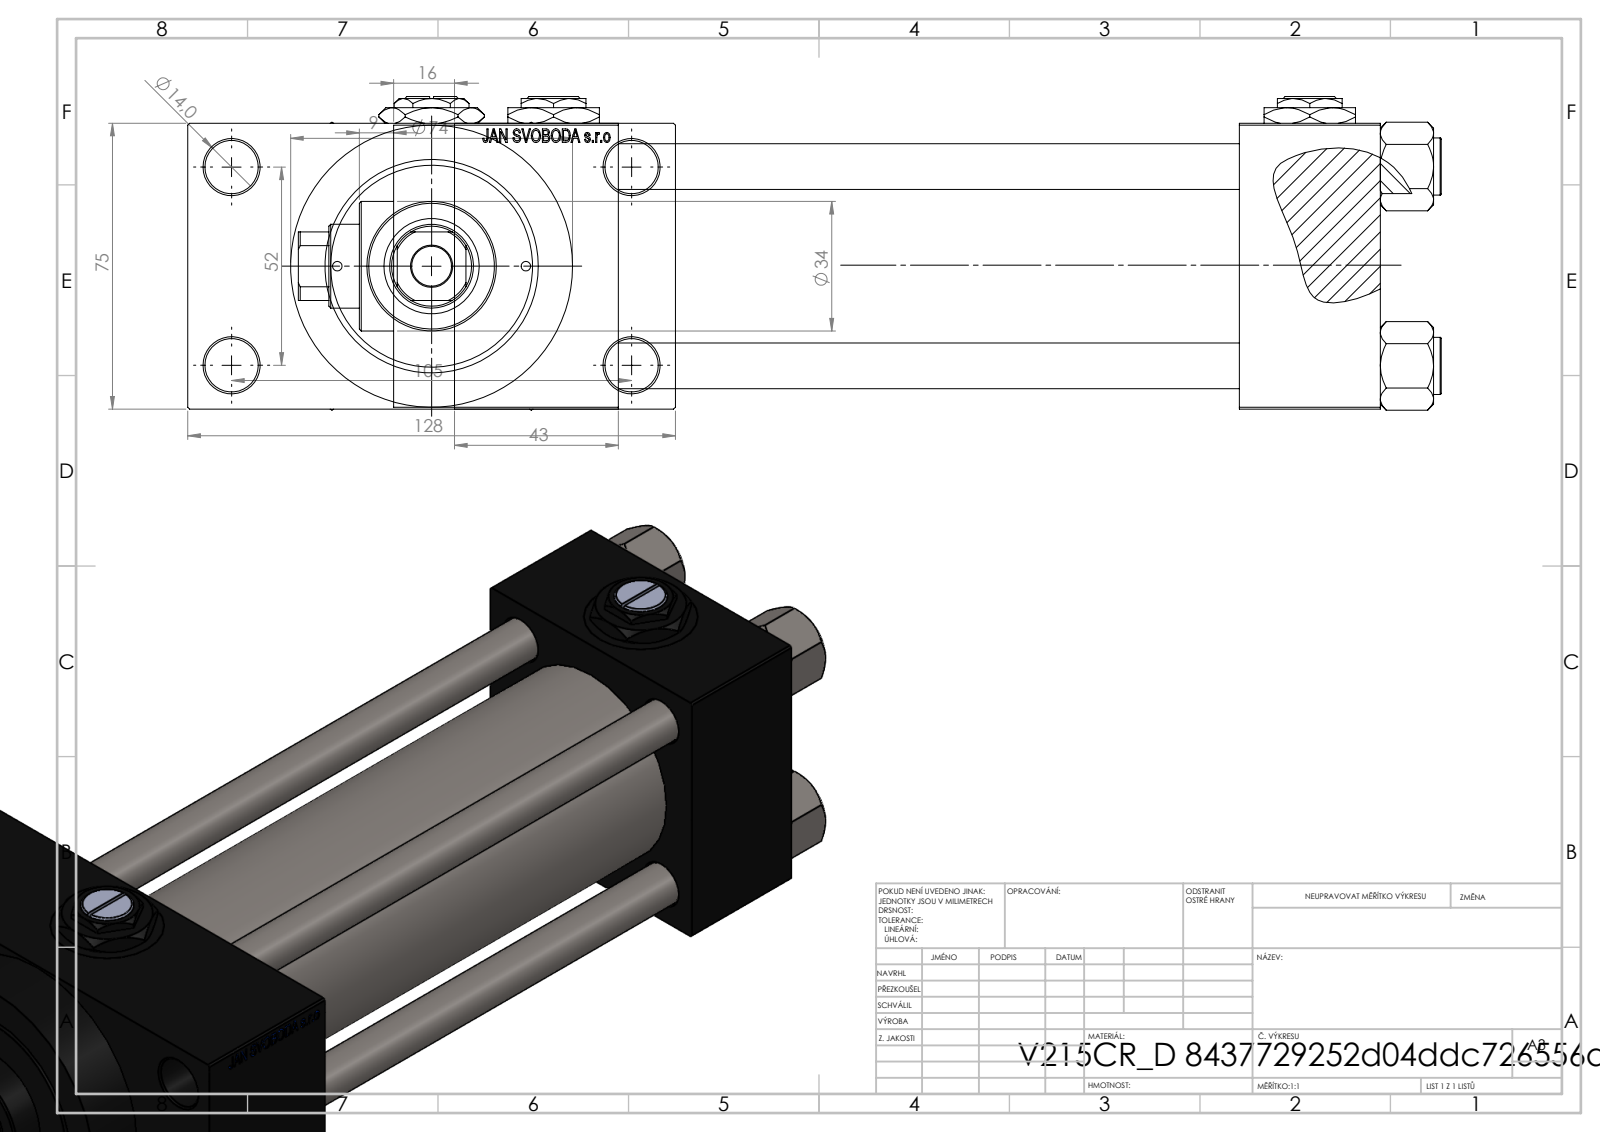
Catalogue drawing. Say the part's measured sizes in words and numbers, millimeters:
The part is named "V215_VC_A; V215CR_D_TYCINKA; V215CR_D_Body; NUT_M5_D (+2 more)". Its 3-D file was written by "SolidWorks 2019 (CONFIG_CONTROL_DESIGN)". It is 13 solids with 1212 faces: 547 planar, 103 cylindrical and 562 other. Overall it measures 300 by 128 by 82.27 millimeters. Its volume is 932 755 cubic millimeters and its surface area 228 913 square millimeters. Round holes: 4 of diameter 12, 4 of diameter 14, 4 of diameter 20.96, 4 of diameter 30, 3 of diameter 7, 2 of diameter 2.5, 1 of diameter 10.5, 1 of diameter 22, 1 of diameter 25, 1 of diameter 41, 1 of diameter 50, 1 of diameter 53. Round bosses or shafts: 4 of diameter 15, 1 of diameter 74, 1 of diameter 56, 1 of diameter 34. Partial cylindrical surfaces (rounded edges, fillets, slot ends): 1 of radius 10.5. The main face-to-face distances are 75, 163, 37, 200, 26.5, 243, 206, 43, 101.5, 16. The hole center spacings are 26.19, 26.35, 36.98, 38.03, 52.3, 57.22, 58.43, 58.59.
